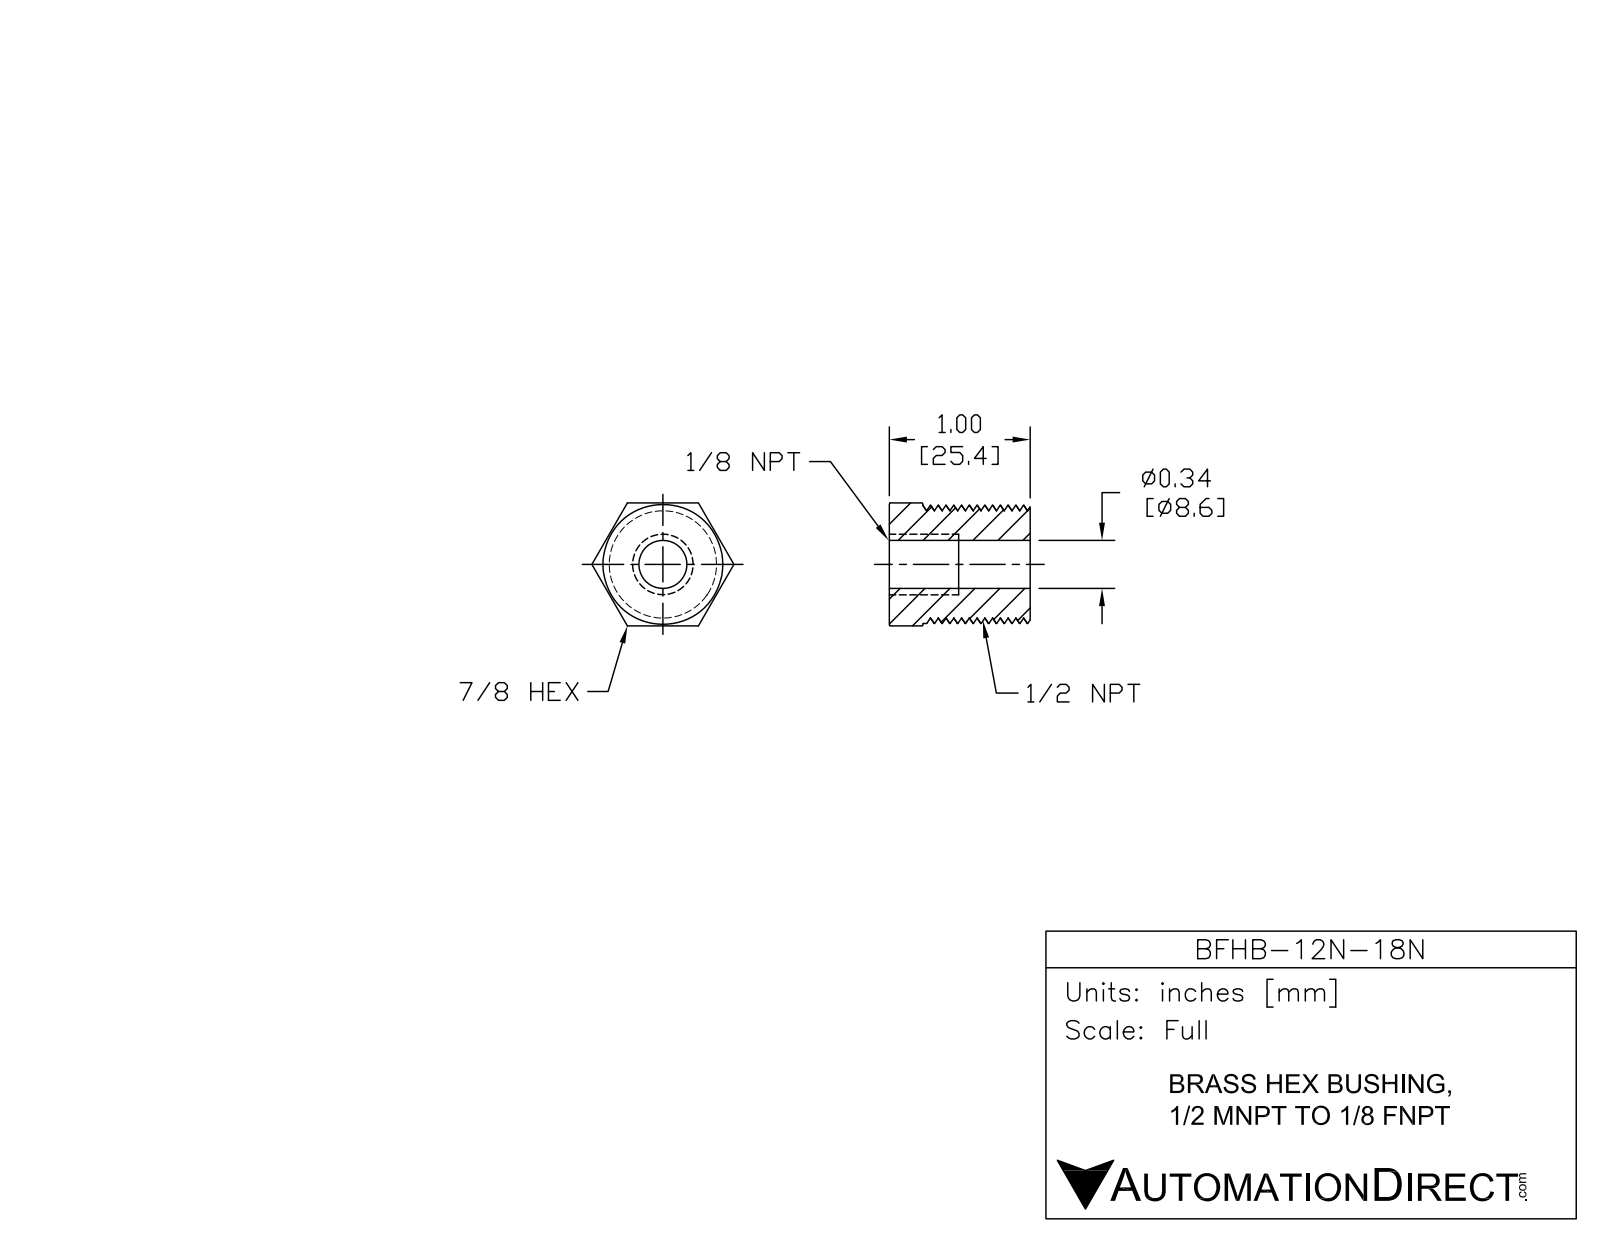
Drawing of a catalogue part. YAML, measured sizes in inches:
part_name: "BFHB-12N-18N"
step_written_by: "SolidWorks 2015 (CONFIG_CONTROL_DESIGN)"
units: inches
bodies: {solids: 1, faces: 48, planar: 10, cylindrical: 31, other: 7}
overall_size: [1.006, 0.997, 0.871]
volume: 0.447
surface_area: 6.075
round_holes:
  - {diameter: 0.34, count: 1}
round_bosses_or_shafts:
  - {diameter: 0.836, count: 1}
face_to_face_distances: [0.997, 0.871, 0.237, 0.76]
